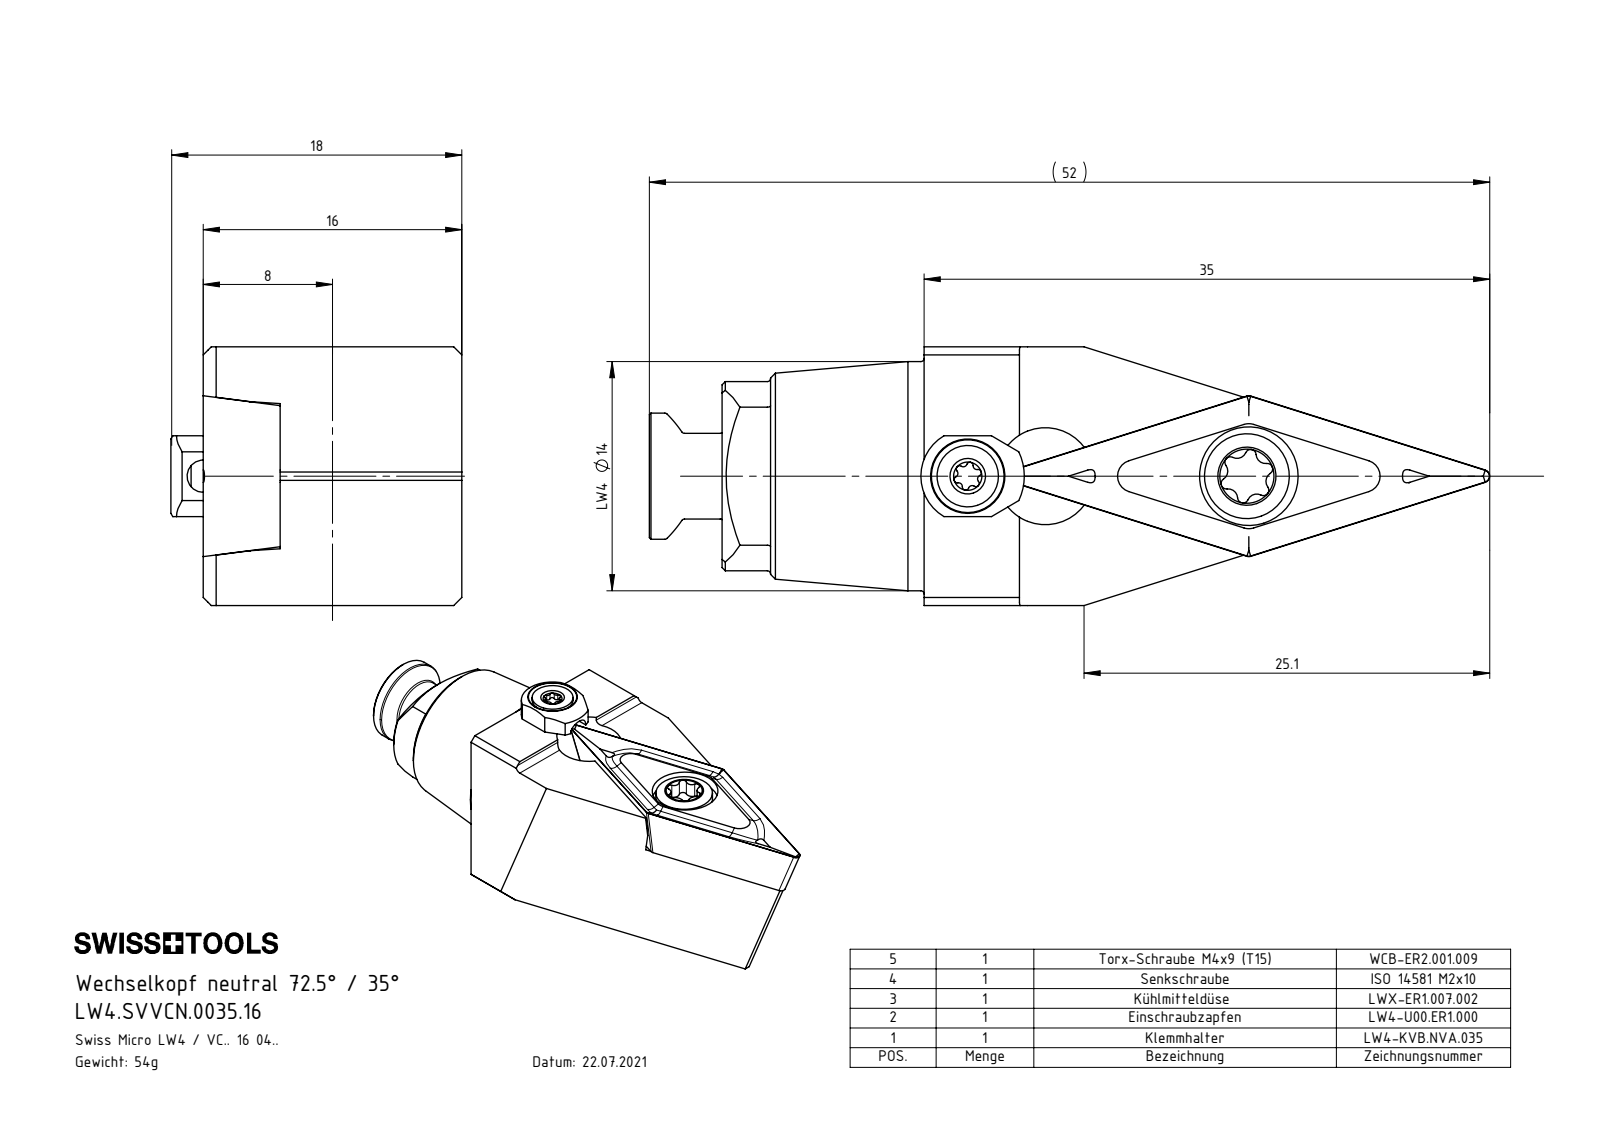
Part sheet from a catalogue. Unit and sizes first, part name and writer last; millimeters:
Units: millimetres
Overall size (bounding box): 52 × 18 × 16
Round holes (diameter × count): ⌀2 ×2, ⌀1.6 ×1, ⌀2.5 ×1, ⌀3 ×1, ⌀3.3 ×1, ⌀4.4 ×1, ⌀5.5 ×1, ⌀6 ×1, ⌀6.1 ×1
Round bosses / shafts (diameter × count): ⌀14.17 ×1, ⌀7.7 ×1, ⌀6 ×1, ⌀5.3 ×1, ⌀5.25 ×1, ⌀5 ×1, ⌀4 ×1, ⌀3.8 ×1
Partial cylindrical surfaces — rounded edges, fillets, slot ends (radius × count): R0.2 ×8, R0.24 ×6, R0.34 ×6, R0.59 ×6, R0.5 ×1, R1 ×1, R2.9 ×1, R3.5 ×1
Main face-to-face distances: 16, 11.24, 4.76, 15.2, 3.96, 0.8, 7.5, 2, 3, 12.5
Hole centre spacings: 4.8, 12.47, 12.59, 17.27, 17.39
Volume: 6 429 mm³ · Surface area: 4 167 mm²
Bodies: 6 solids, 269 faces (71 planar, 82 cylindrical, 116 other)
Part name (STEP PRODUCT): ISO 14581 - M2x10; LW4-U00.ER1.000_B; WCB-ER2.001.009_A; LWX-ER1.007.002 (+3 more)
STEP written by: SolidWorks 2022 (CONFIG_CONTROL_DESIGN)
